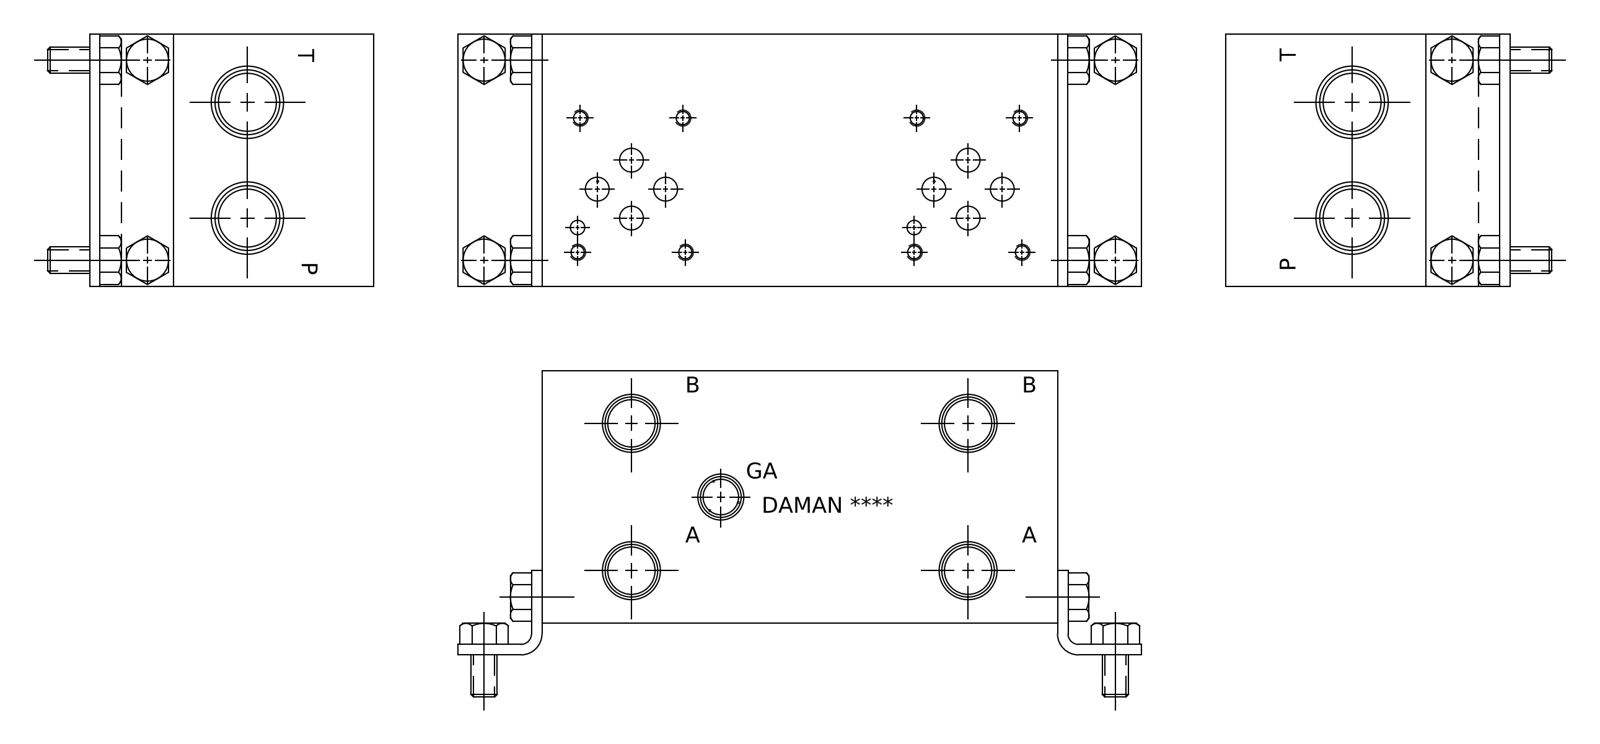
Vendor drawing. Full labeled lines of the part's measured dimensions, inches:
Part name (STEP PRODUCT): D03P024P
STEP written by: Autodesk Inventor 2021 (AUTOMOTIVE_DESIGN)
Units: inches
Bodies: 1 solid, 583 faces (356 planar, 52 cylindrical, 175 other)
Overall size (bounding box): 6.125 × 3 × 3
Volume: 52.4 in³ · Surface area: 110.1 in²
Round holes (diameter × count): ⌀0.149 ×8, ⌀0.19 ×8, ⌀0.281 ×6, ⌀0.563 ×4, ⌀0.681 ×4, ⌀0.156 ×2, ⌀0.25 ×2, ⌀0.257 ×2, ⌀0.312 ×2, ⌀0.625 ×2, ⌀0.85 ×2, ⌀0.422 ×1
Main face-to-face distances: 3, 6.125, 0.605, 0.605, 5.52, 4.915, 5.52, 0.462, 2.538, 0.46
Hole centre spacings: 4, 0.785, 0.868, 1.321, 1.594, 2.026, 0.295, 0.511
